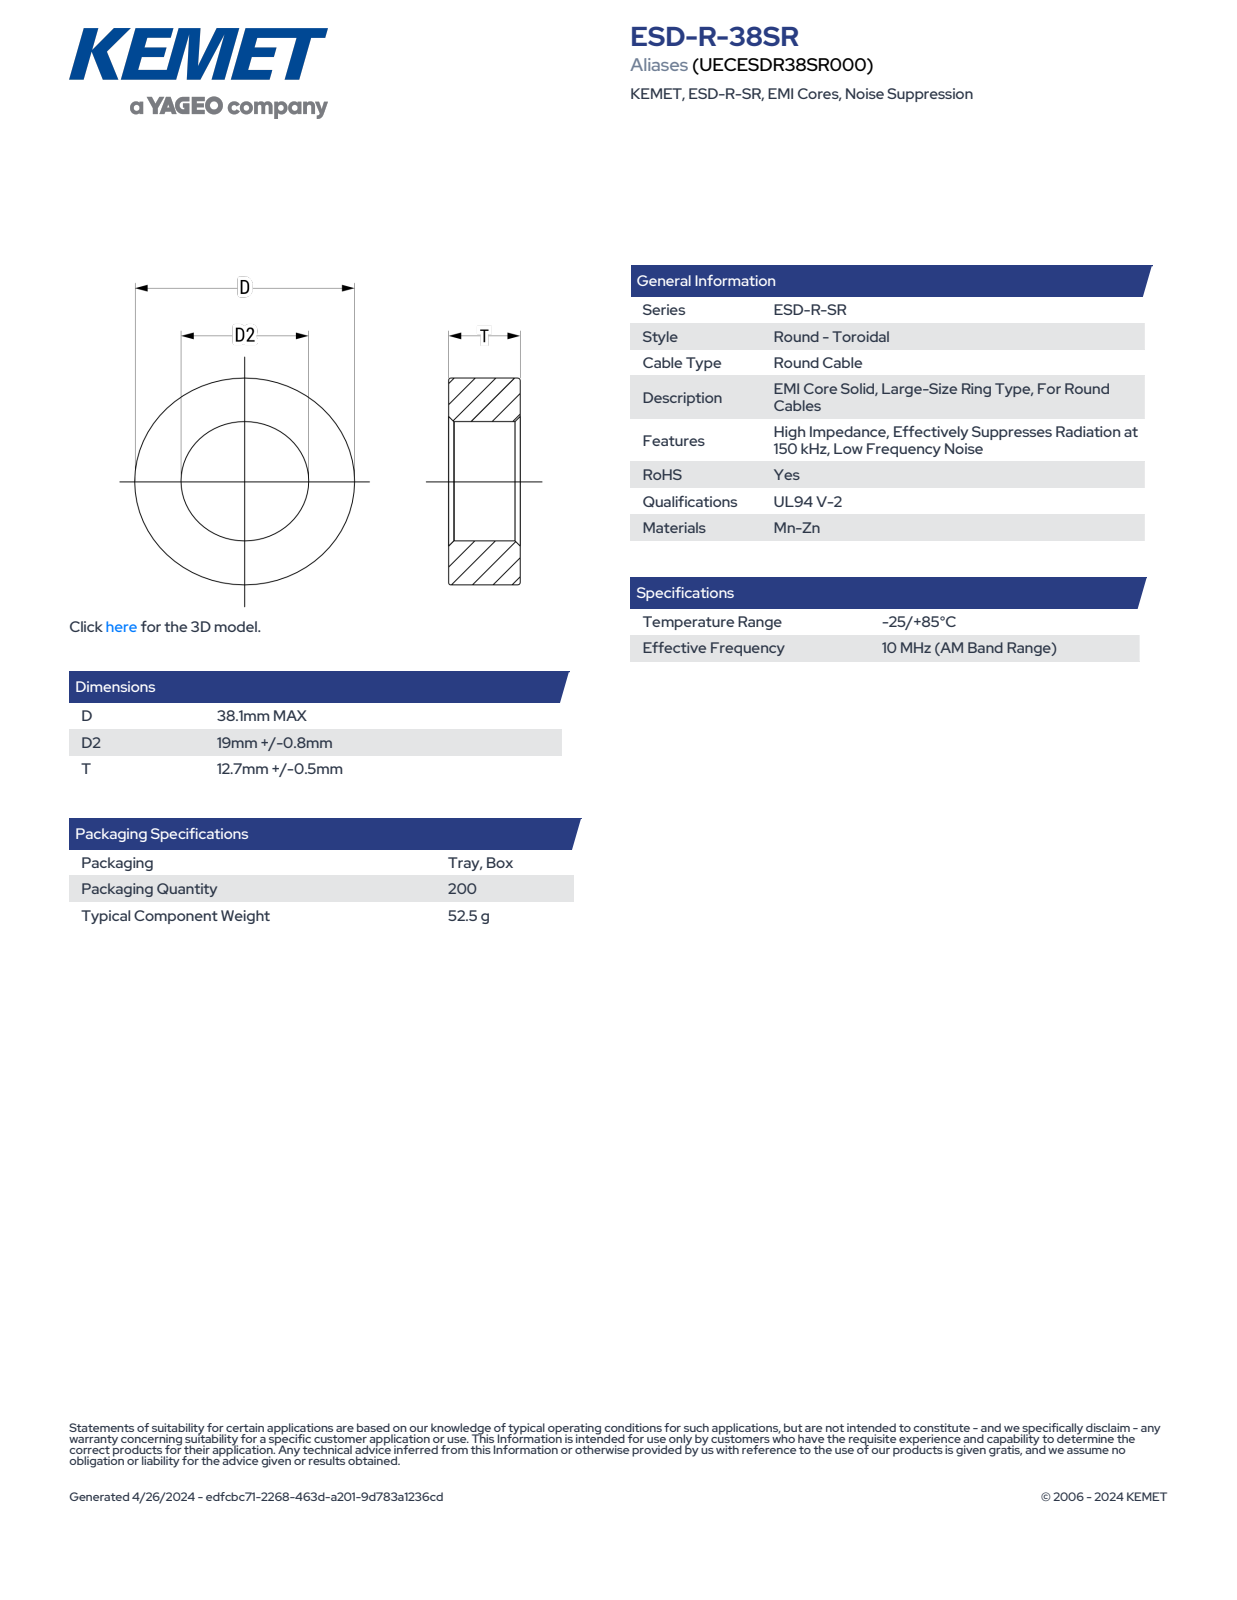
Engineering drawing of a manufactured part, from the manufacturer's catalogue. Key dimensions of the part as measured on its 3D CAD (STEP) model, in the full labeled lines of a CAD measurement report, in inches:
Part name (STEP PRODUCT): EC_ESDRSR_D38.1D219T13.2
STEP written by: SolidWorks 2021 (AUTOMOTIVE_DESIGN)
Units: inches
Bodies: 1 solid, 70 faces (24 planar, 7 cylindrical, 39 other)
Overall size (bounding box): 1.5 × 1.5 × 0.52
Volume: 0.682 in³ · Surface area: 6.028 in²
Round holes (diameter × count): ⌀0.748 ×1
Round bosses / shafts (diameter × count): ⌀1.5 ×1
Partial cylindrical surfaces — rounded edges, fillets, slot ends (radius × count): R0.75 ×1
Main face-to-face distances: 0.52, 0.161, 0.359, 0.198, 0.321, 0.038, 0.235, 0.075, 0.086, 0.124
